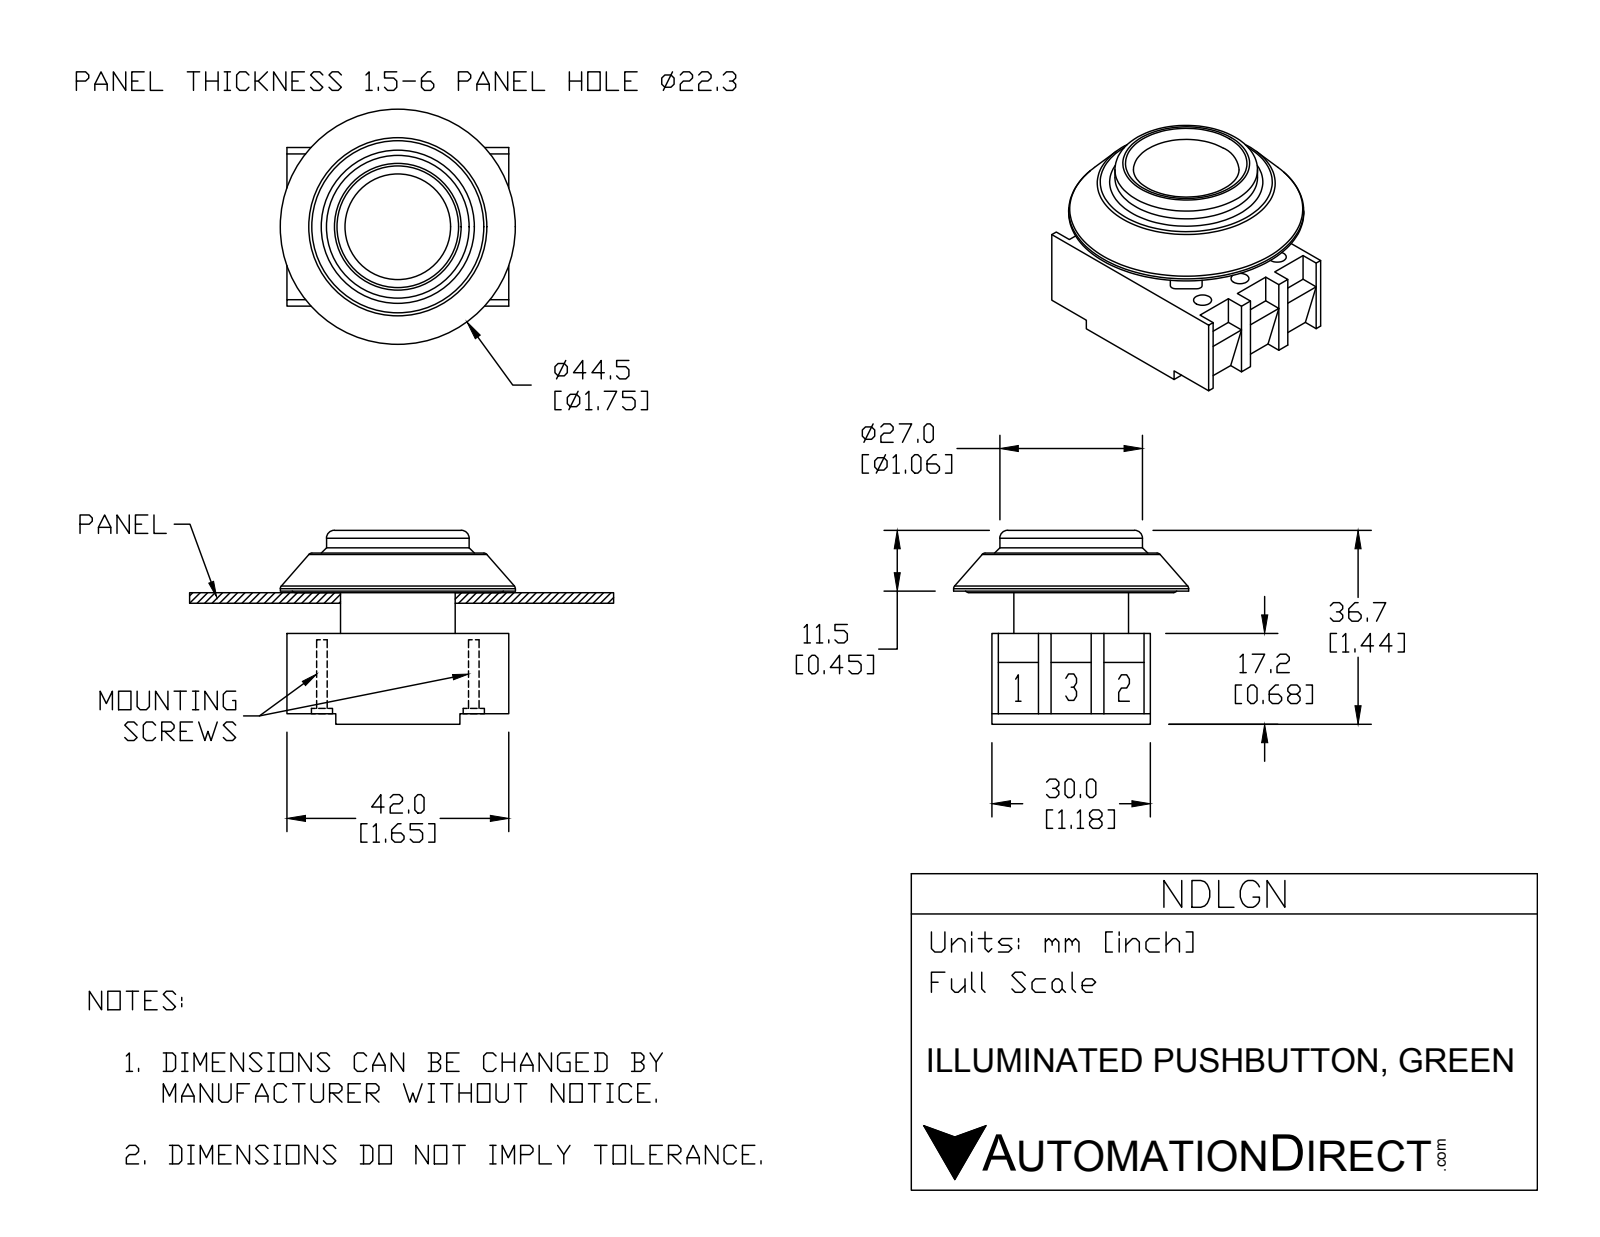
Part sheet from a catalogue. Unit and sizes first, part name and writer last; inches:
Units: inches
Overall size (bounding box): 1.752 × 1.752 × 1.445
Round holes (diameter × count): ⌀0.134 ×6, ⌀0.197 ×6, ⌀0.492 ×1
Round bosses / shafts (diameter × count): ⌀0.181 ×2, ⌀0.157 ×2, ⌀1.752 ×1, ⌀1.063 ×1, ⌀0.854 ×1
Partial cylindrical surfaces — rounded edges, fillets, slot ends (radius × count): R0.039 ×8, R0.343 ×5, R0.433 ×1
Main face-to-face distances: 0.283, 0.598, 1.181, 0.394, 0.315, 0.295, 0.303, 0.406, 0.709, 0.913
Hole centre spacings: 0.394, 0.69, 1.199, 1.132, 0.566, 0.787, 1.379
Volume: 1.533 in³ · Surface area: 25.91 in²
Bodies: 7 solids, 217 faces (127 planar, 65 cylindrical, 25 other)
Part name (STEP PRODUCT): NDLGN
STEP written by: SolidWorks 2015 (AUTOMOTIVE_DESIGN)
